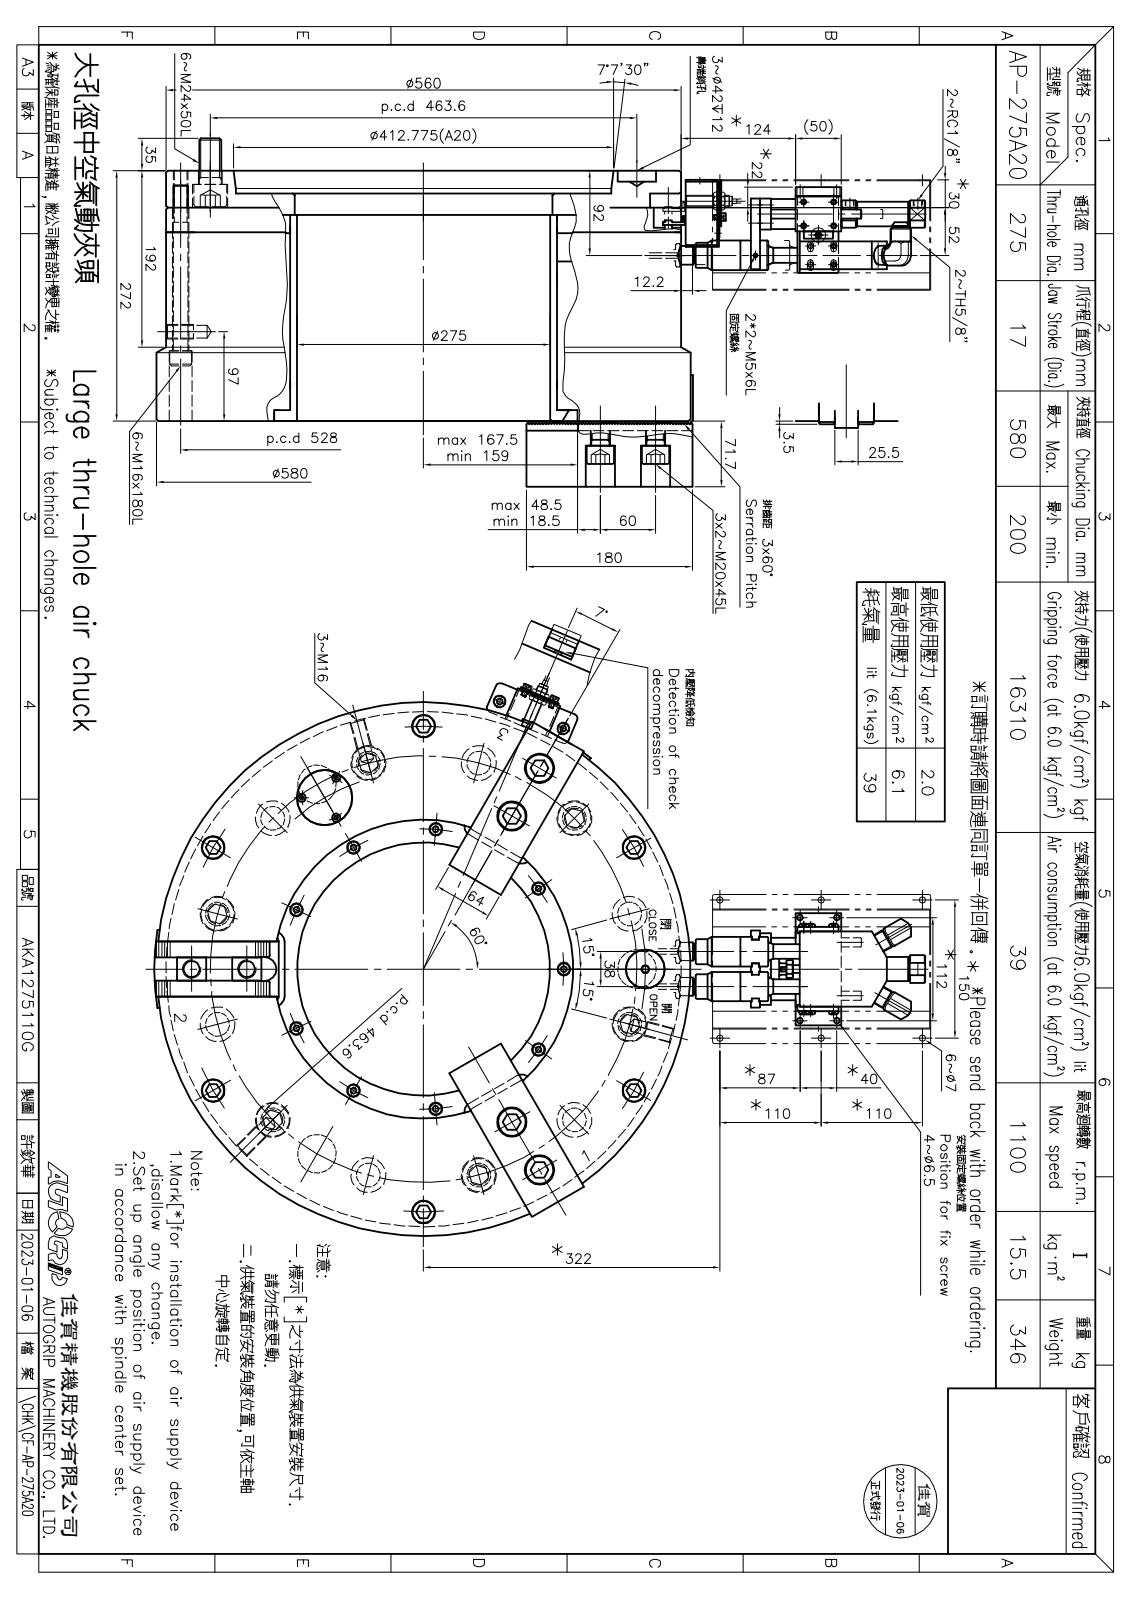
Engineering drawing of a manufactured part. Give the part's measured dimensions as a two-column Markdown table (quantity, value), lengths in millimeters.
| quantity | value |
| --- | --- |
| part name | 圓頭內六角螺栓_M16x180; CF-AP-275A20; CF-AP-275-07000; 圓頭內六角螺栓_M14x40 (+8 more) |
| STEP written by | SolidWorks 2016 (CONFIG_CONTROL_DESIGN) |
| units | millimeters |
| bodies | 51 solids, 4575 faces (3211 planar, 1004 cylindrical, 360 other) |
| overall size | 606 × 580 × 378.7 |
| volume | 51 680 000 mm³ |
| surface area | 3 090 000 mm² |
| round holes (diameter × count) | 14 × 28, 26 × 18, 38 × 18, 23 × 15, 15 × 14, 9 × 11, 6.8 × 9, 17.5 × 6, 25 × 6, 8 × 5, 42 × 3, 7.5 × 2 |
| round bosses / shafts (diameter × count) | 24 × 12, 21 × 12, 14 × 11, 13 × 9, 16 × 8, 36 × 6, 30 × 6, 20 × 6 |
| partial cylindrical surfaces (radius × count) | 0.1 × 309, 20 × 3 |
| main face-to-face distances | 27, 232, 205, 40, 67, 272, 15, 25, 42, 247 |
| hole center spacings | 264, 152.5, 174.94, 264.14, 152.38, 304.88, 128.9, 373.01 |
